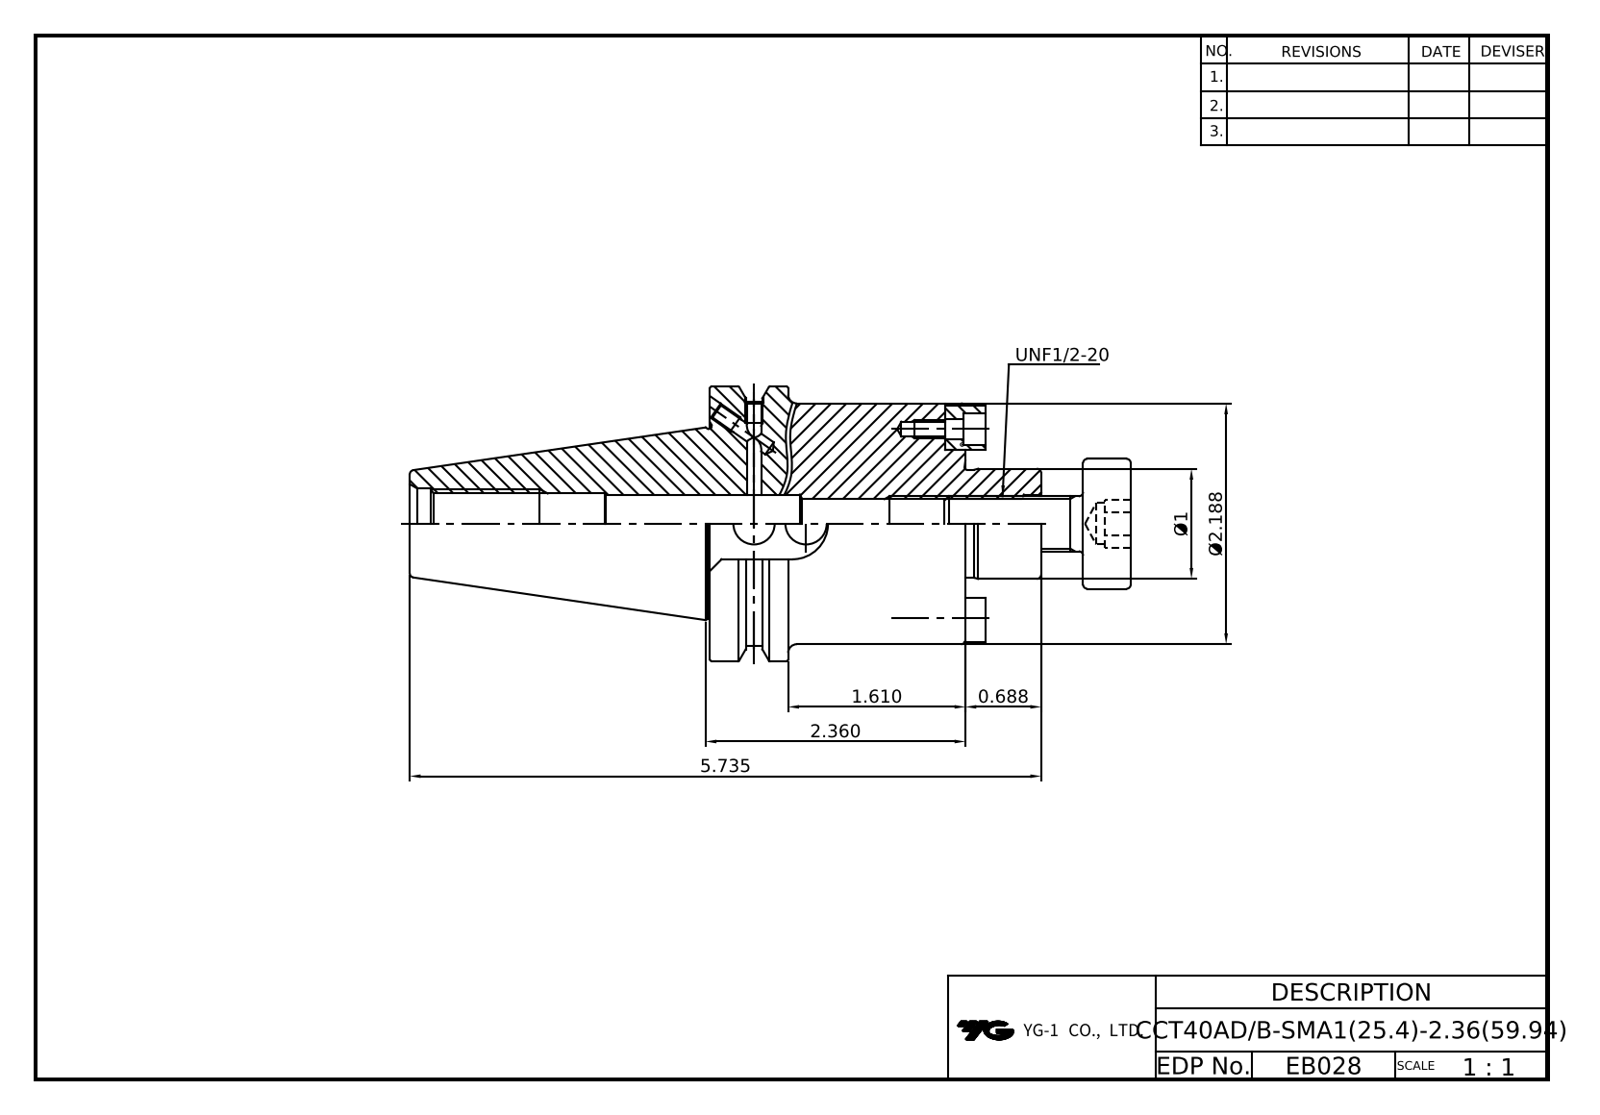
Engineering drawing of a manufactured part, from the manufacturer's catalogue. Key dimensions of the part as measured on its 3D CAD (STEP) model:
Part name (STEP PRODUCT): LO-CCT40ADB-SMA25.4-59.944; DRIVE KEY-9.52x9.52x10.2; HEX'' WRENCH BOLT-UNC#8-32x3_8L; COLLAR BOLT-UNF1_2-20x32L
STEP written by: Autodesk Inventor 2022 (AUTOMOTIVE_DESIGN)
Units: inches
Bodies: 6 solids, 179 faces (87 planar, 49 cylindrical, 43 other)
Overall size (bounding box): 6.365 × 2.5 × 2.405
Volume: 13.2 in³ · Surface area: 58.74 in²
Round holes (diameter × count): ⌀0.128 ×4, ⌀0.13 ×2, ⌀0.157 ×2, ⌀0.165 ×2, ⌀0.177 ×2, ⌀0.295 ×2, ⌀0.375 ×2, ⌀0.446 ×1, ⌀0.512 ×1, ⌀0.527 ×1, ⌀0.531 ×1, ⌀0.642 ×1
Round bosses / shafts (diameter × count): ⌀0.27 ×2, ⌀0.164 ×2, ⌀2.5 ×1, ⌀2.188 ×1, ⌀1.724 ×1, ⌀1.181 ×1, ⌀1 ×1, ⌀0.98 ×1
Partial cylindrical surfaces — rounded edges, fillets, slot ends (radius × count): R0.187 ×2, R0.322 ×1, R1.108 ×1
Main face-to-face distances: 2.32, 3.639, 1.318, 0.375, 3.206, 0.885, 0.433, 1.874, 2.133, 0.188
Hole centre spacings: 0.86, 1.72
